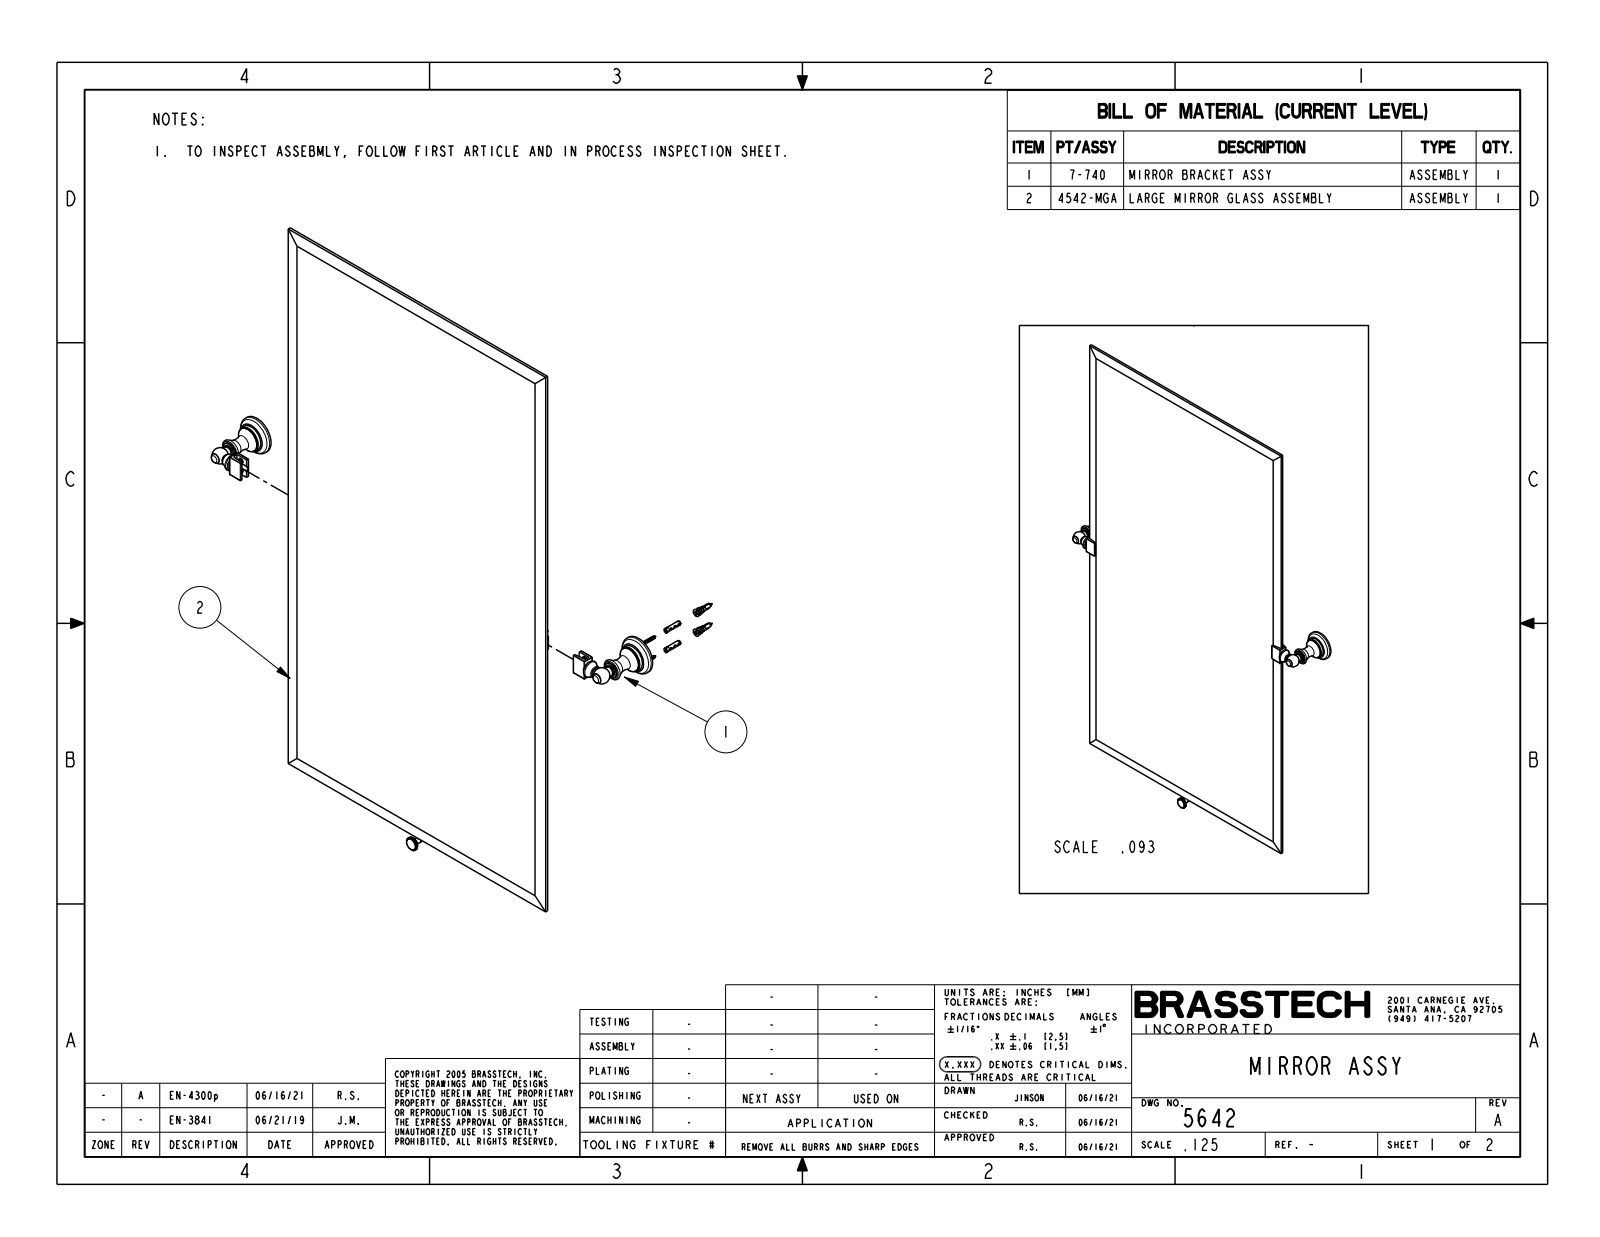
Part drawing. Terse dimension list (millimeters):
name: 5642
written by: CREO PARAMETRIC BY PTC INC, 2018400 (CONFIG_CONTROL_DESIGN)
unit: mm
bodies: 1 solid, 631 faces (259 planar, 110 cylindrical, 262 other)
size: 929.3 × 622.3 × 86.6
volume: 2 887 000 mm³; area: 987 700 mm²
holes: 2× ⌀34.8
bosses: 2× ⌀55.9, 2× ⌀37.8, 2× ⌀36.1, 2× ⌀34.3, 2× ⌀22.9, 2× ⌀16.8, 2× ⌀14.2, 2× ⌀13.1
rounds: 24× R0.3, 20× R0.8, 8× R1, 2× R0.6
face distances: 6, 1, 7, 69.6, 70.6, 76.6, 31.5, 441, 442, 472.4
hole spacings: 566.4
